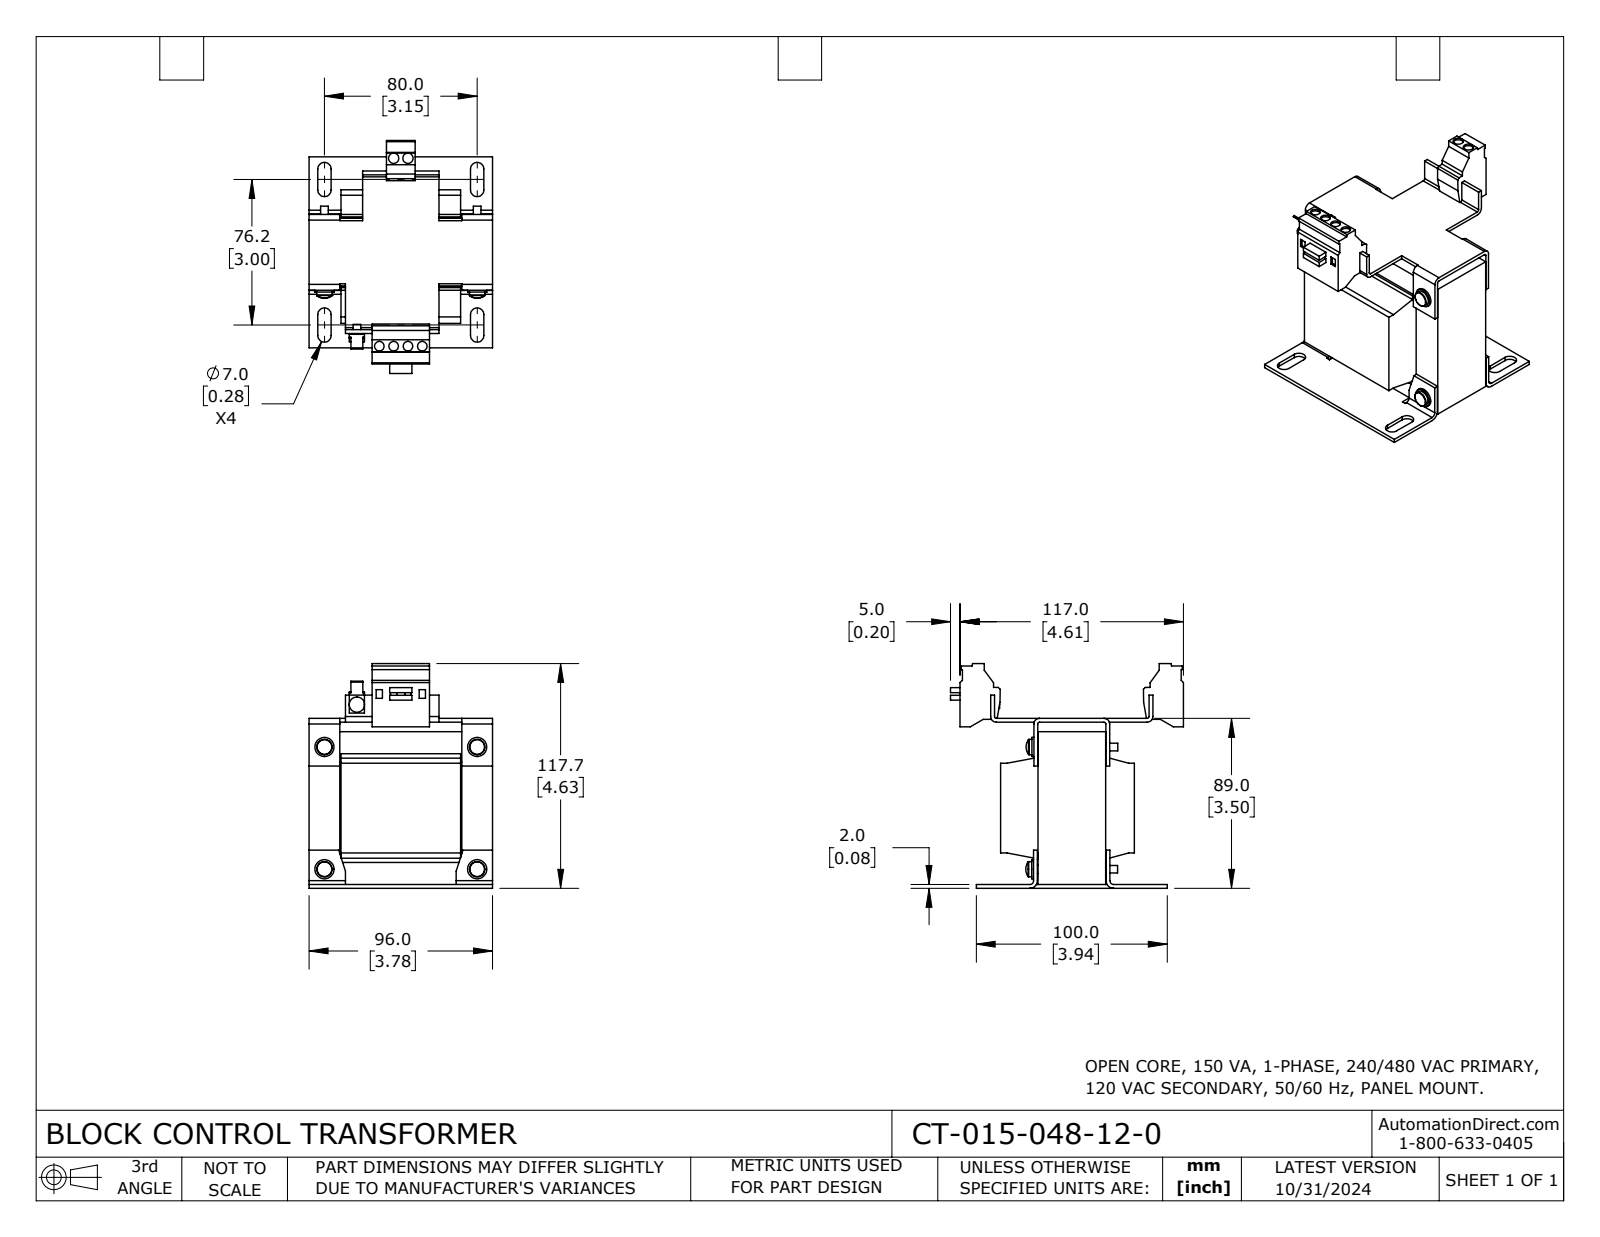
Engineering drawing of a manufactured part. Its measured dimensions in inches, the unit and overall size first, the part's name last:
Units: inches
Overall size (bounding box): 4.803 × 4.634 × 3.78
Round holes (diameter × count): ⌀0.197 ×4, ⌀0.213 ×2
Round bosses / shafts (diameter × count): ⌀0.315 ×5, ⌀0.157 ×5, ⌀0.394 ×4, ⌀0.177 ×4
Partial cylindrical surfaces — rounded edges, fillets, slot ends (radius × count): R0.138 ×8, R0.039 ×4, R0.118 ×4, R0.079 ×2, R0.157 ×2
Main face-to-face distances: 0.079, 3.425, 3.15, 0.657, 3.122, 0.63, 3.346, 3.504, 1.398, 2.52
Hole centre spacings: 0.295, 3.885, 0.591, 3.874, 3.919, 0.886
Volume: 26.58 in³ · Surface area: 135.7 in²
Bodies: 1 solid, 341 faces (241 planar, 88 cylindrical, 12 other)
Part name (STEP PRODUCT): CT-015-048-12-0
STEP written by: SolidWorks 2023 (CONFIG_CONTROL_DESIGN)
